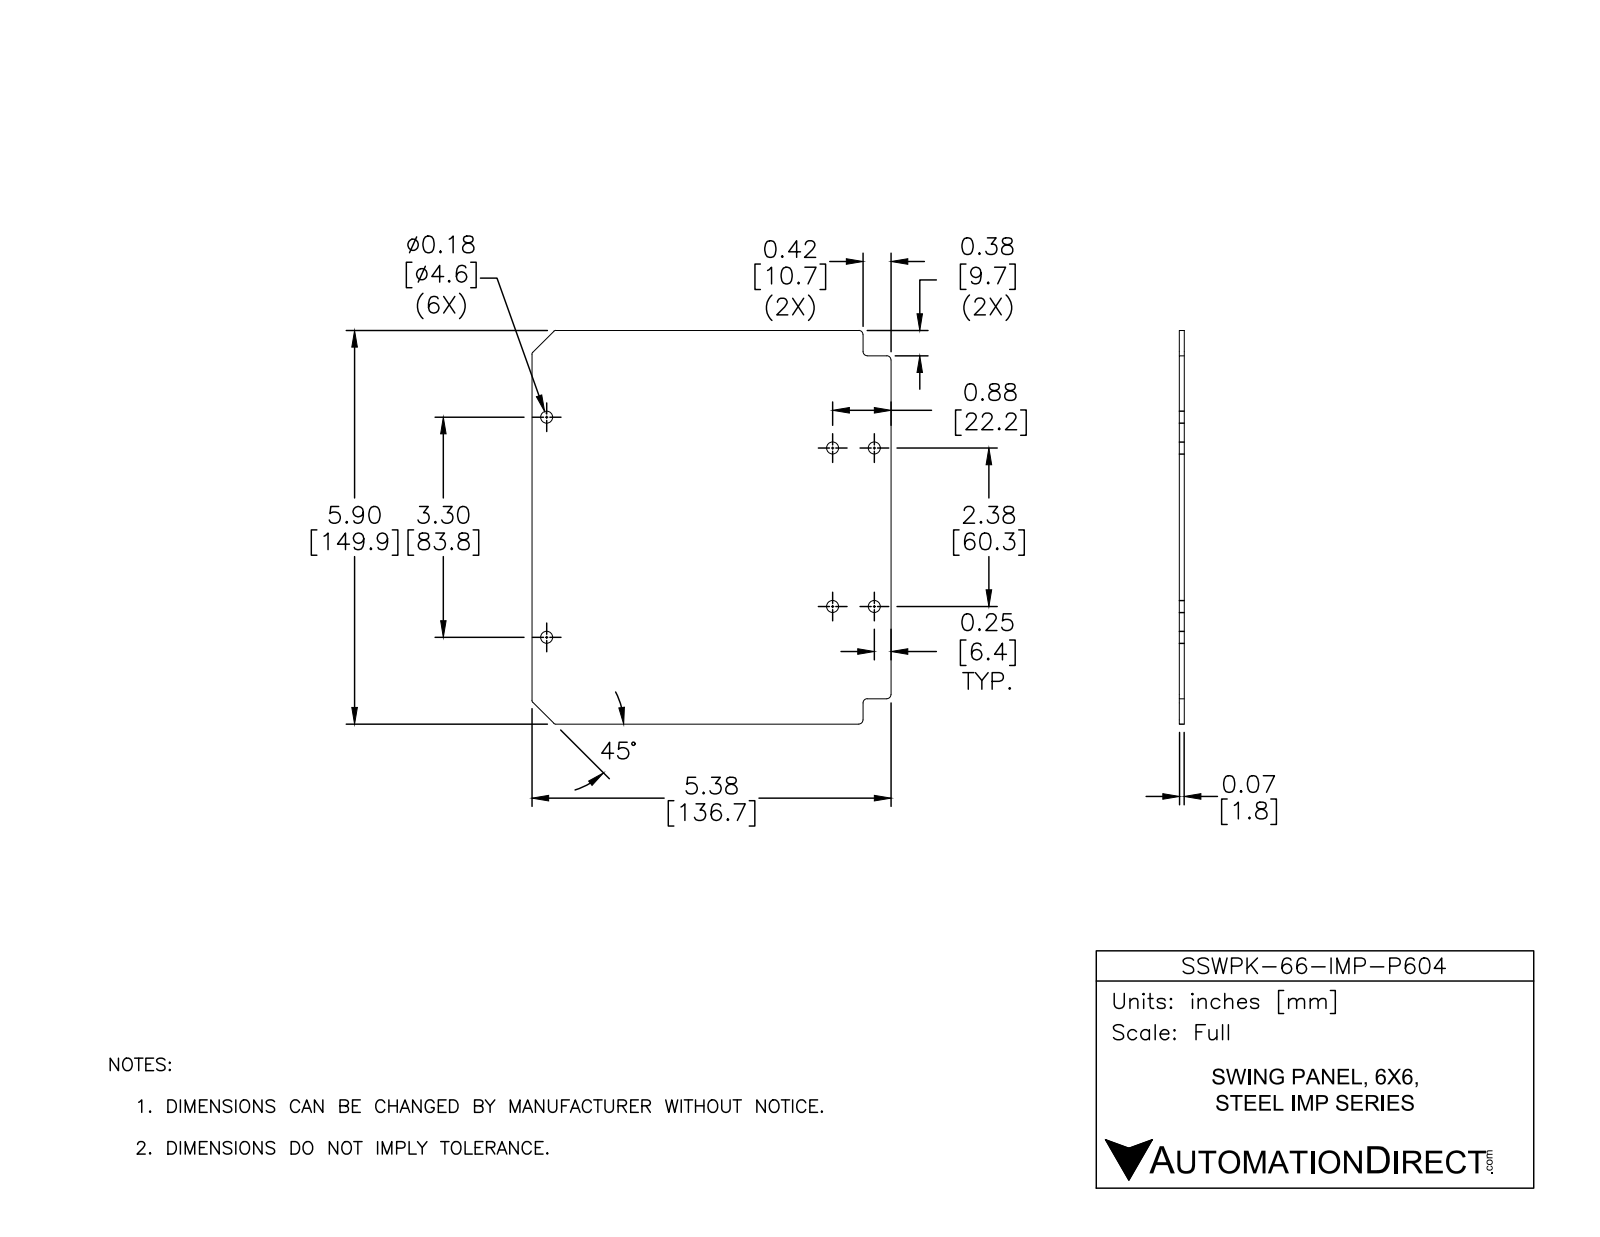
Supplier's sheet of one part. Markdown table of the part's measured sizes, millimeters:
| quantity | value |
| --- | --- |
| part name | SSWPK-66-IMP-P604 |
| STEP written by | SolidWorks 2016 (AUTOMOTIVE_DESIGN) |
| units | millimeters |
| bodies | 1 solid, 34 faces (12 planar, 22 cylindrical, 0 other) |
| overall size | 149.9 × 136.7 × 1.6 |
| volume | 32 740 mm³ |
| surface area | 41 270 mm² |
| round holes (diameter × count) | 4.6 × 6 |
| partial cylindrical surfaces (radius × count) | 1.6 × 6, 1 × 4 |
| main face-to-face distances | 1.6, 136.7, 149.9, 9.7, 140.2, 126.1, 10.7, 130.6 |
| hole center spacings | 15.9, 60.3, 62.4, 109.5, 125.3, 130.6, 144.1, 83.8 |
